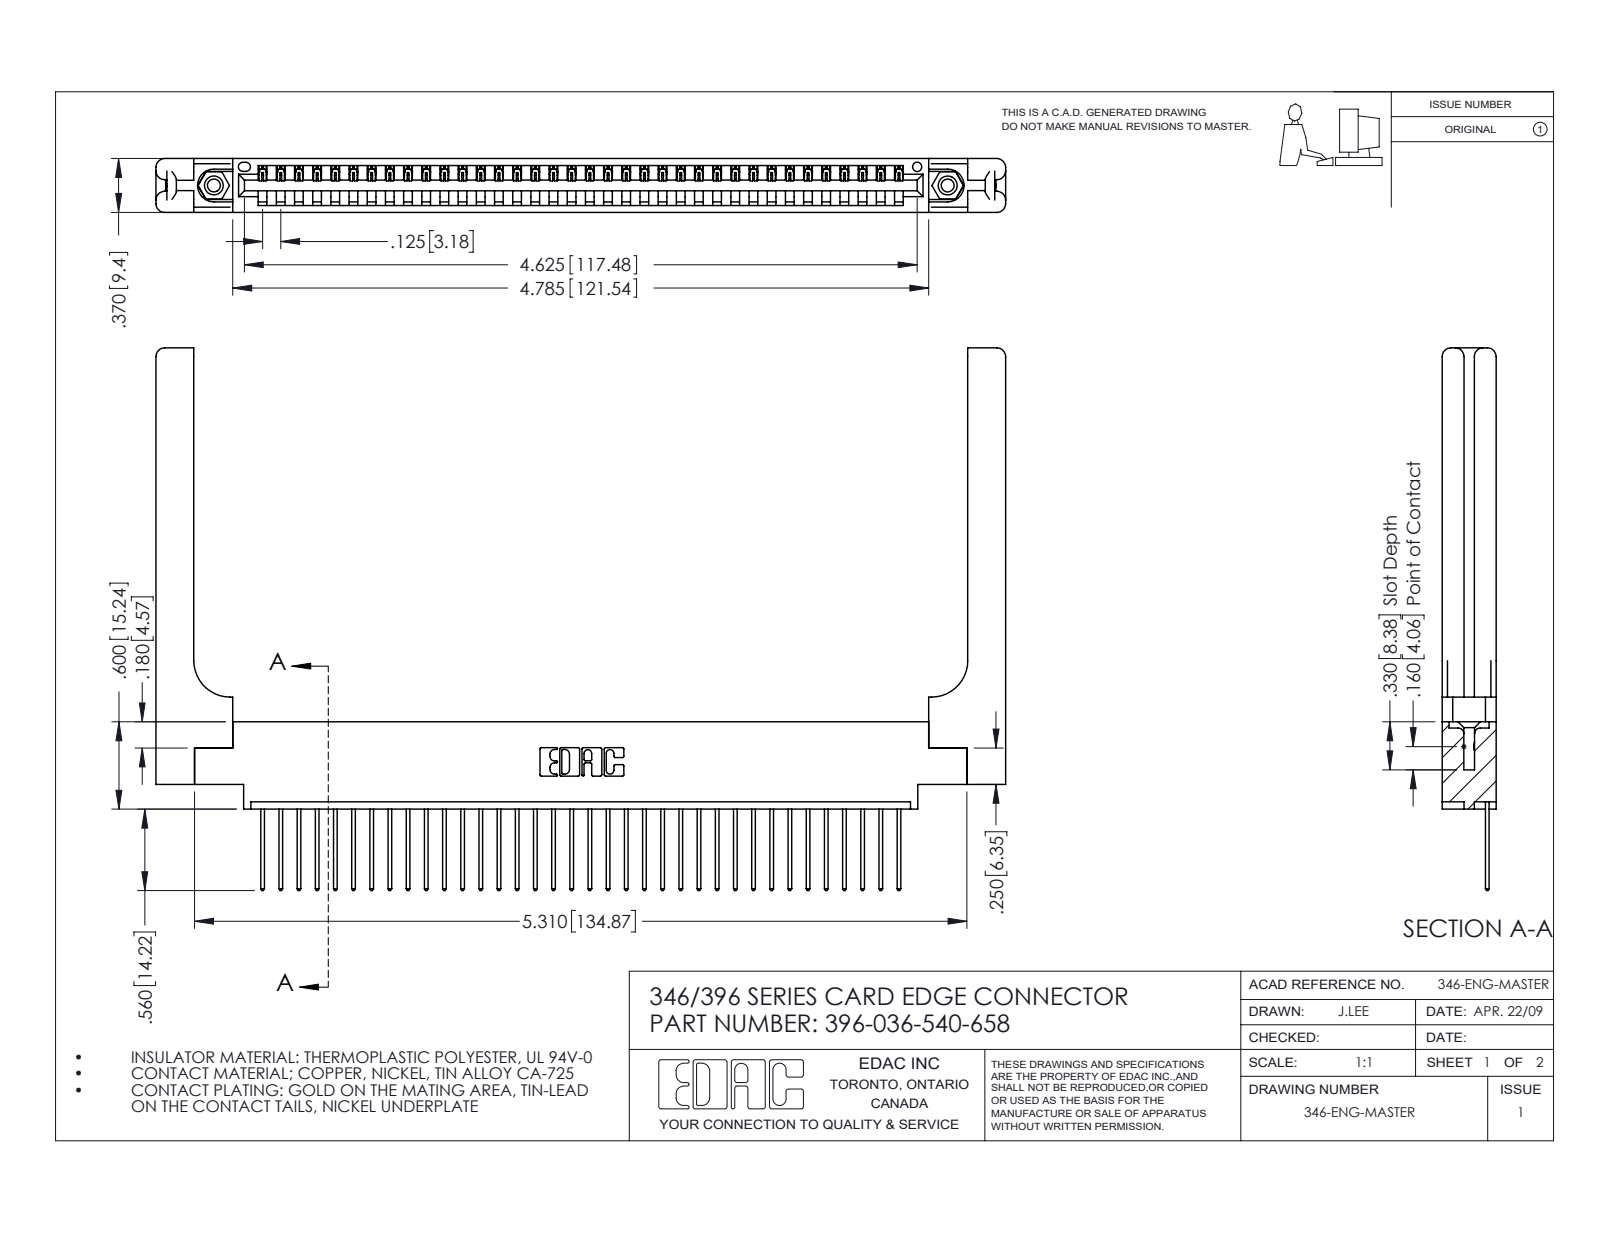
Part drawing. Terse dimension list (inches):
name: 396-036-540-658; 345-250-001_345-250-001-102; 345-292-001_345-293-140; 346 Part_0.170 Offset - 0.156 Dia-TH (+1 more)
written by: SolidWorks 2016 (CONFIG_CONTROL_DESIGN)
unit: in
bodies: 41 solids, 2470 faces (1668 planar, 742 cylindrical, 60 other)
size: 5.841 × 3.73 × 0.37
volume: 1.316 in³; area: 35.94 in²
holes: 2× ⌀0.089, 2× ⌀0.125, 2× ⌀0.156, 1× ⌀0.064
bosses: 2× ⌀0.155
rounds: 72× R0.006, 72× R0.01, 22× R0.01, 16× R0.06, 6× R0.007, 6× R0.031, 3× R0.026, 2× R0.03
face distances: 0.37, 0.048, 0.322, 0.072, 0.148, 0.15, 0.25, 0.298, 0.025, 0.222
hole spacings: 0.246, 4.836, 5.045
